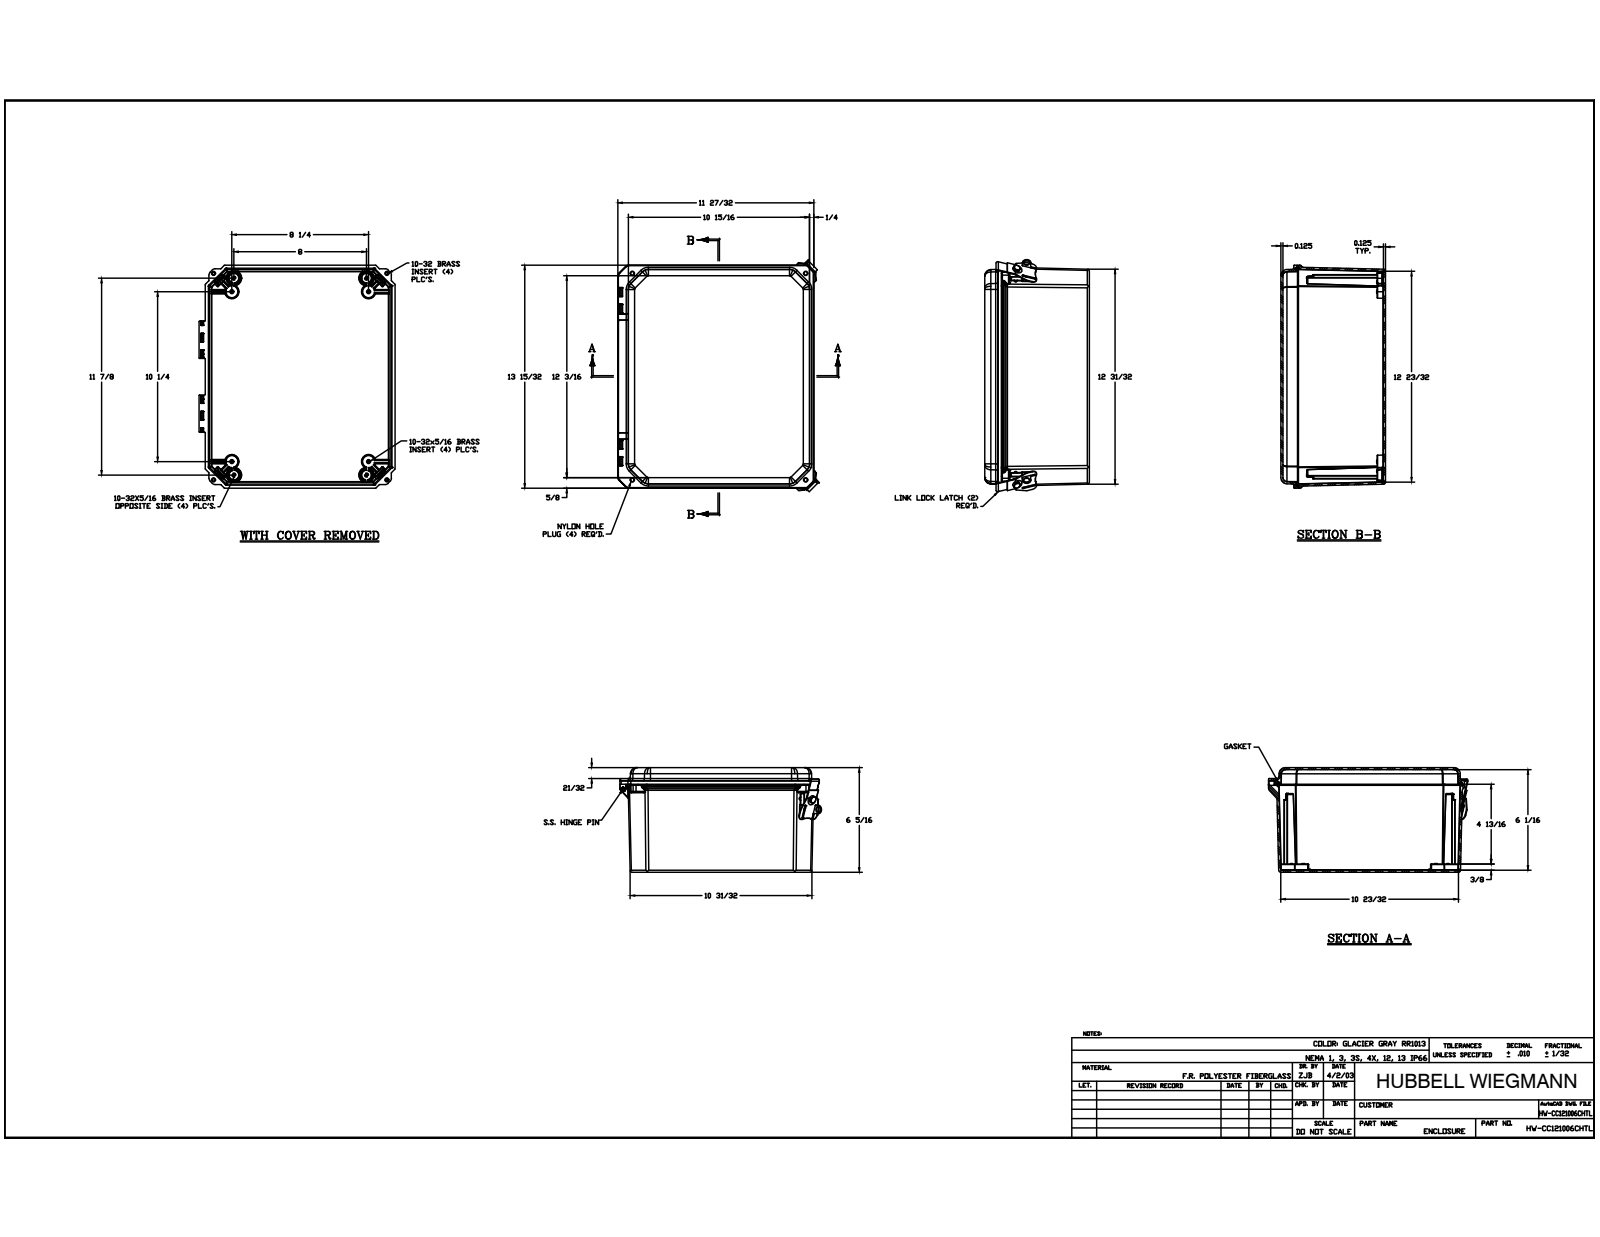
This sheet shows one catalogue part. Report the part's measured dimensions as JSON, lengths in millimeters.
{"part_name": "DS121006BOX; DSCC121006CVR; GA1210; WP1210HLU (+5 more)", "step_written_by": "Autodesk Inventor 2014 (AUTOMOTIVE_DESIGN)", "units": "millimeters", "bodies": {"solids": 31, "faces": 2283, "planar": 661, "cylindrical": 890, "other": 732}, "overall_size": [364.13, 311.71, 160.32], "volume_mm3": 1387000, "surface_area_mm2": 820577, "round_holes": [[3.96, 12], [3.86, 8], [3.81, 4], [5.56, 4], [6.4, 4], [7.92, 4], [1.27, 2], [2.49, 2], [3.05, 2], [9.22, 2], [3.48, 1]], "round_bosses_or_shafts": [[6.25, 12], [22.1, 4], [5.3, 4], [1.27, 4], [3.43, 3], [15.24, 2], [5.08, 2]], "partial_cylinders_radius": [[0.25, 208], [0.13, 94], [0.51, 59], [3.17, 41], [0.76, 37], [0.99, 28], [6.35, 26], [0.76, 24]], "face_to_face_distances": [3.17, 157.15, 160.32, 153.98, 3.53, 3.55, 3.56, 140.49, 16.66, 25.4], "hole_center_spacings": [289.7, 373.58, 387.84, 20.92, 281.04, 348.66, 32.02, 39.6]}
